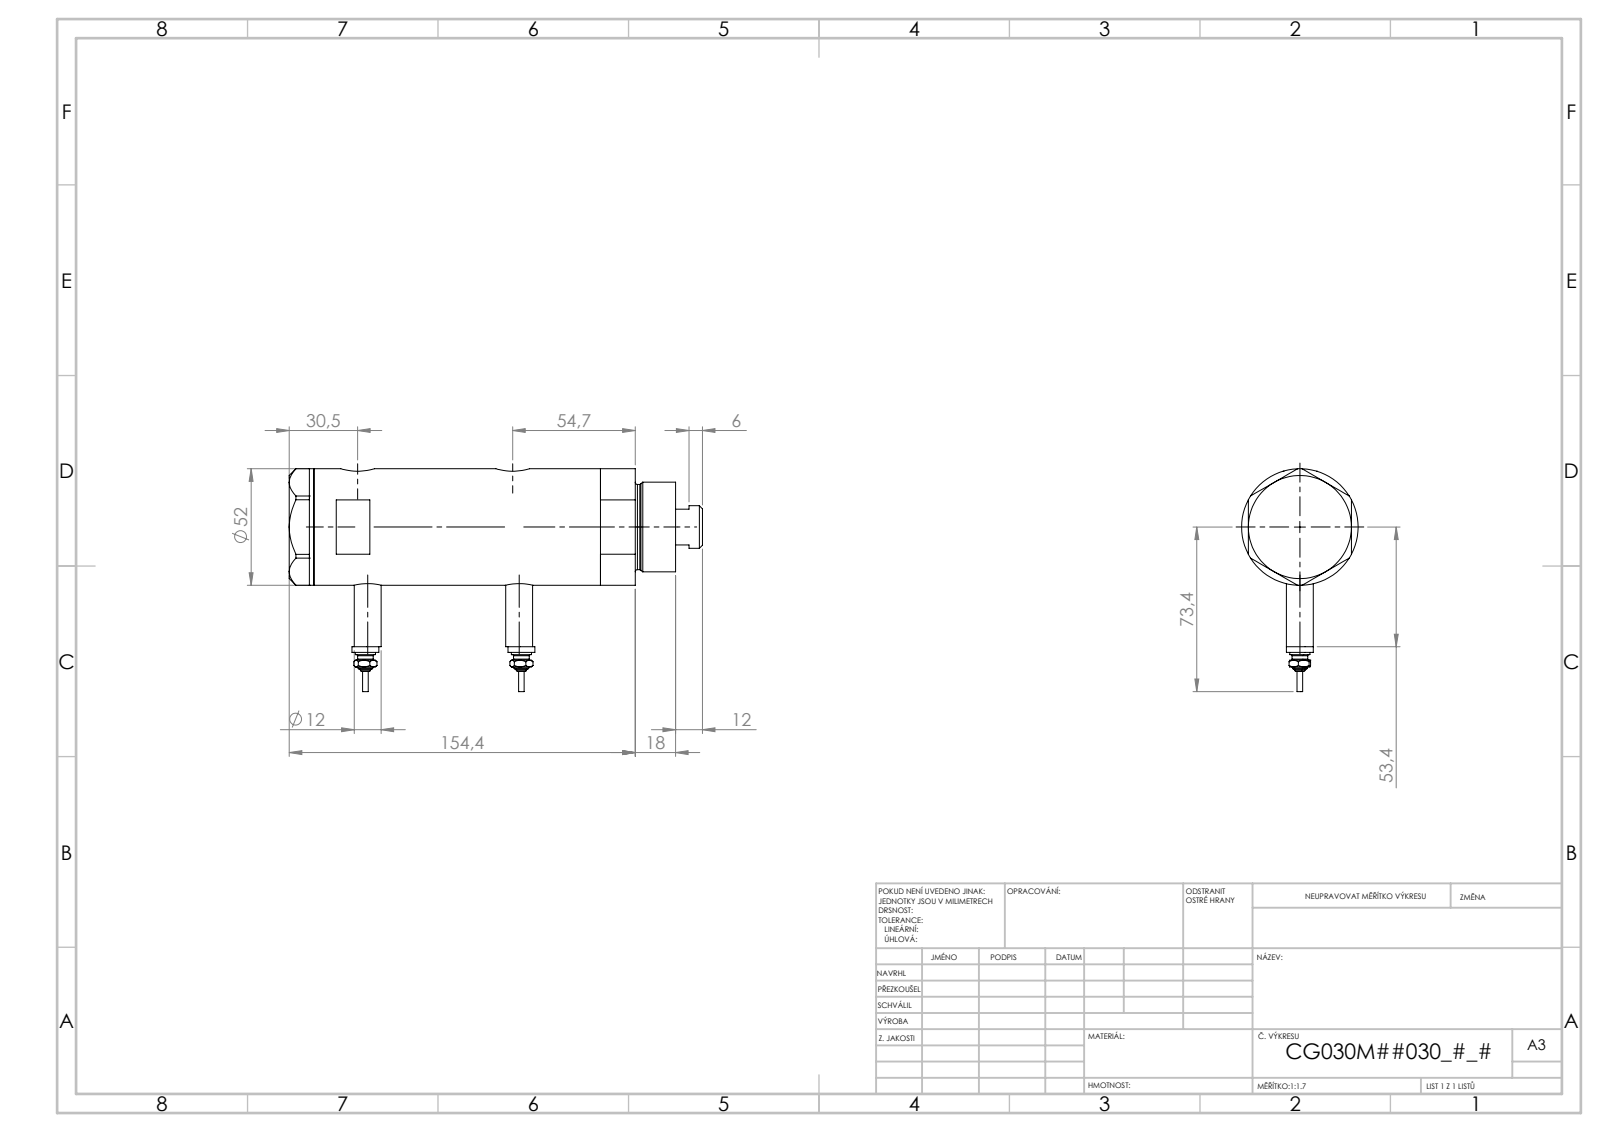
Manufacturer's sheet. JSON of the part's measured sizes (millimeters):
{"part_name": "V270CG_SWITCH; V270CG_MIDDLE; V270CG_BACK; V270CG_VC (+1 more)", "step_written_by": "SolidWorks 2019 (CONFIG_CONTROL_DESIGN)", "units": "millimeters", "bodies": {"solids": 6, "faces": 246, "planar": 95, "cylindrical": 77, "other": 74}, "overall_size": [179.02, 84.3, 52], "volume_mm3": 322306, "surface_area_mm2": 76649, "round_holes": [[5, 2], [9.73, 2], [12.5, 2], [15, 2], [6.5, 1], [20, 1], [21.5, 1], [30, 1], [33, 1], [44, 1]], "round_bosses_or_shafts": [[12, 3], [9, 2], [7, 2], [4.34, 2], [2.4, 2], [52, 1], [40, 1], [38, 1]], "face_to_face_distances": [23.81, 10.99, 34.8, 46, 94.55, 83.56, 59.75, 130.95, 119.96, 96.15], "hole_center_spacings": [2.9, 4.5, 56.75, 59.65, 61.25, 64.15, 2.89, 2.91]}
